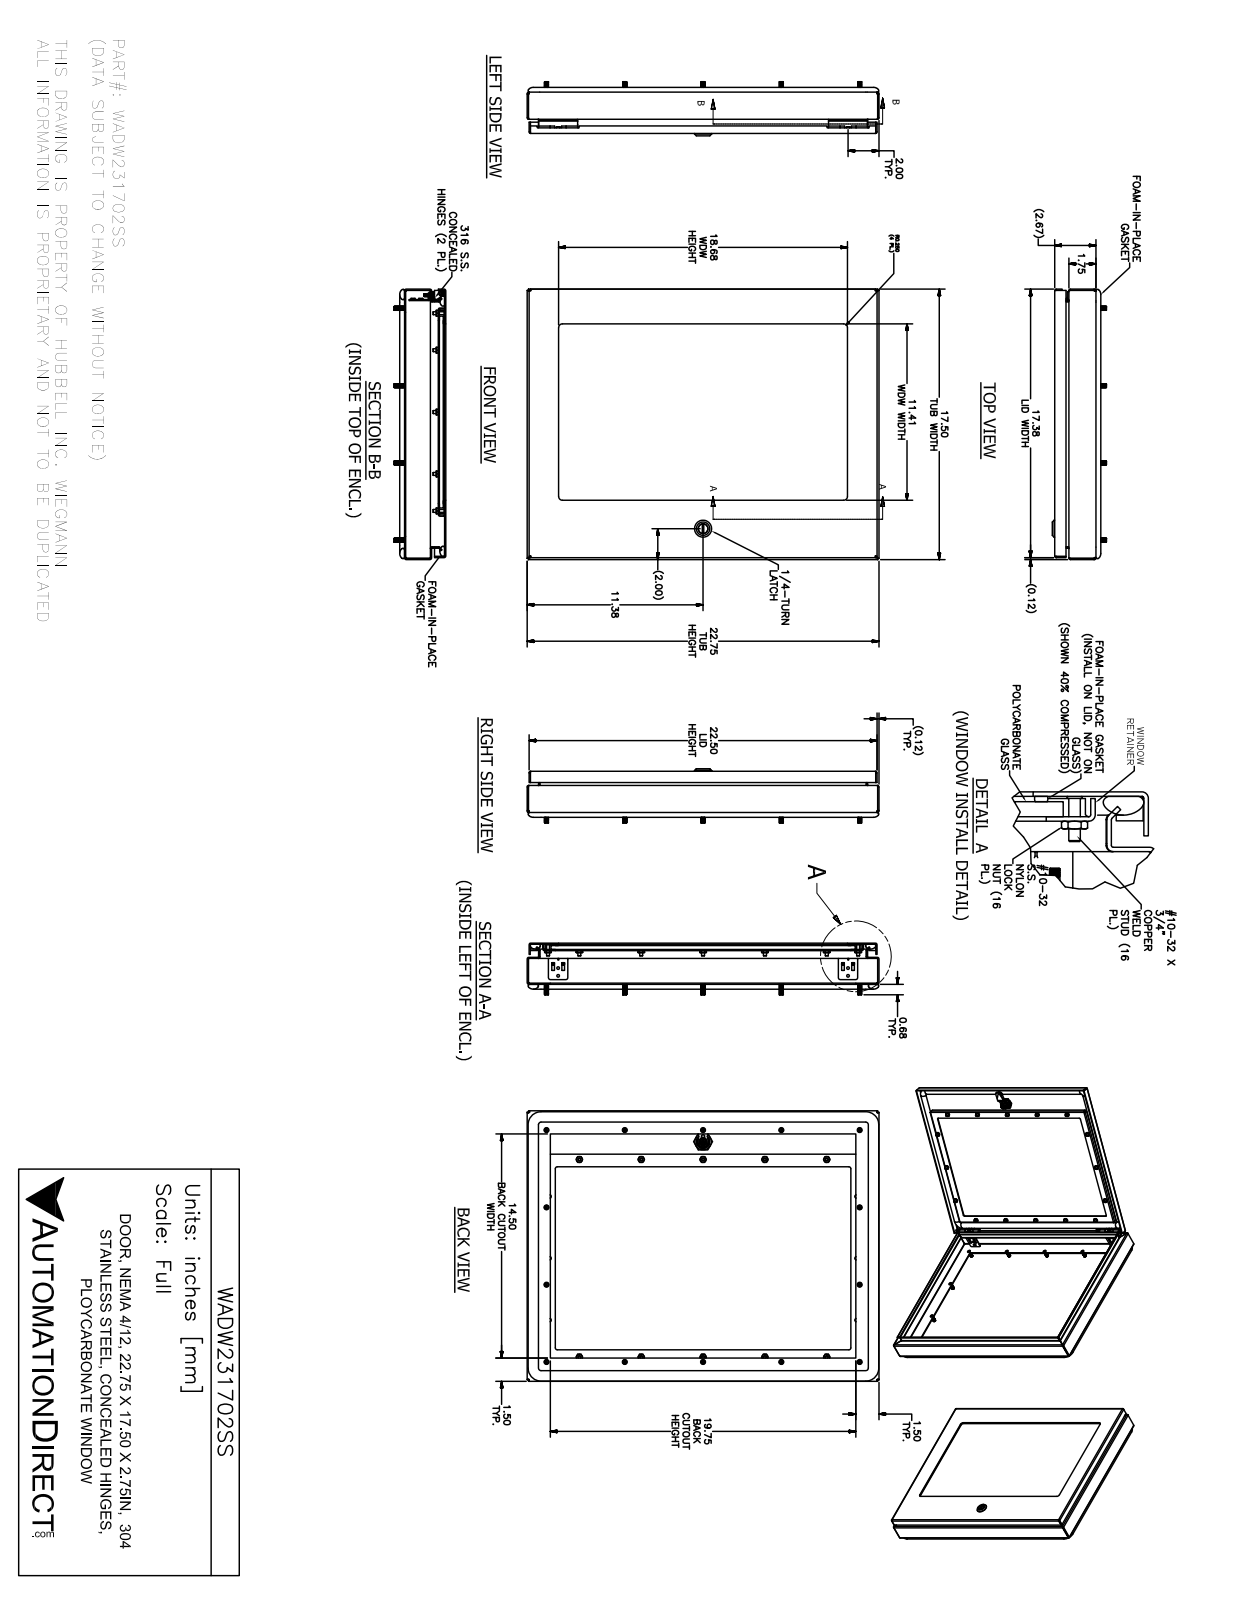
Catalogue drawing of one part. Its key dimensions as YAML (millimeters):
part_name: "WADW231702SS"
step_written_by: "SolidWorks 2017 (AUTOMOTIVE_DESIGN)"
units: millimeters
bodies: {solids: 76, faces: 2095, planar: 776, cylindrical: 648, other: 671}
overall_size: [577.9, 444.5, 88.9]
volume: 2270000
surface_area: 1365000
round_holes:
  - {diameter: 4, count: 18}
  - {diameter: 7.1, count: 16}
  - {diameter: 6.3, count: 12}
  - {diameter: 2.4, count: 4}
  - {diameter: 3.9, count: 4}
  - {diameter: 4.2, count: 4}
  - {diameter: 4.4, count: 4}
  - {diameter: 4.8, count: 4}
  - {diameter: 4.7, count: 1}
  - {diameter: 5, count: 1}
  - {diameter: 8, count: 1}
  - {diameter: 10, count: 1}
round_bosses_or_shafts:
  - {diameter: 6.4, count: 24}
  - {diameter: 4.8, count: 16}
  - {diameter: 9.1, count: 4}
  - {diameter: 8.1, count: 4}
  - {diameter: 6.5, count: 4}
  - {diameter: 4.2, count: 4}
  - {diameter: 3.3, count: 4}
  - {diameter: 8, count: 2}
partial_cylinders:
  - {radius: 0.8, count: 34}
  - {radius: 0.3, count: 30}
  - {radius: 1.3, count: 26}
  - {radius: 2.7, count: 24}
  - {radius: 3.2, count: 20}
  - {radius: 0.4, count: 18}
  - {radius: 0.5, count: 13}
  - {radius: 0.8, count: 8}
face_to_face_distances: [1.9, 6.4, 8.6, 2.2, 10.4, 4.1, 65.9, 55.4, 61.8, 64]
hole_center_spacings: [101.6, 203.2, 340.3, 383.1, 324.7, 476.1, 170.3, 304.8]
